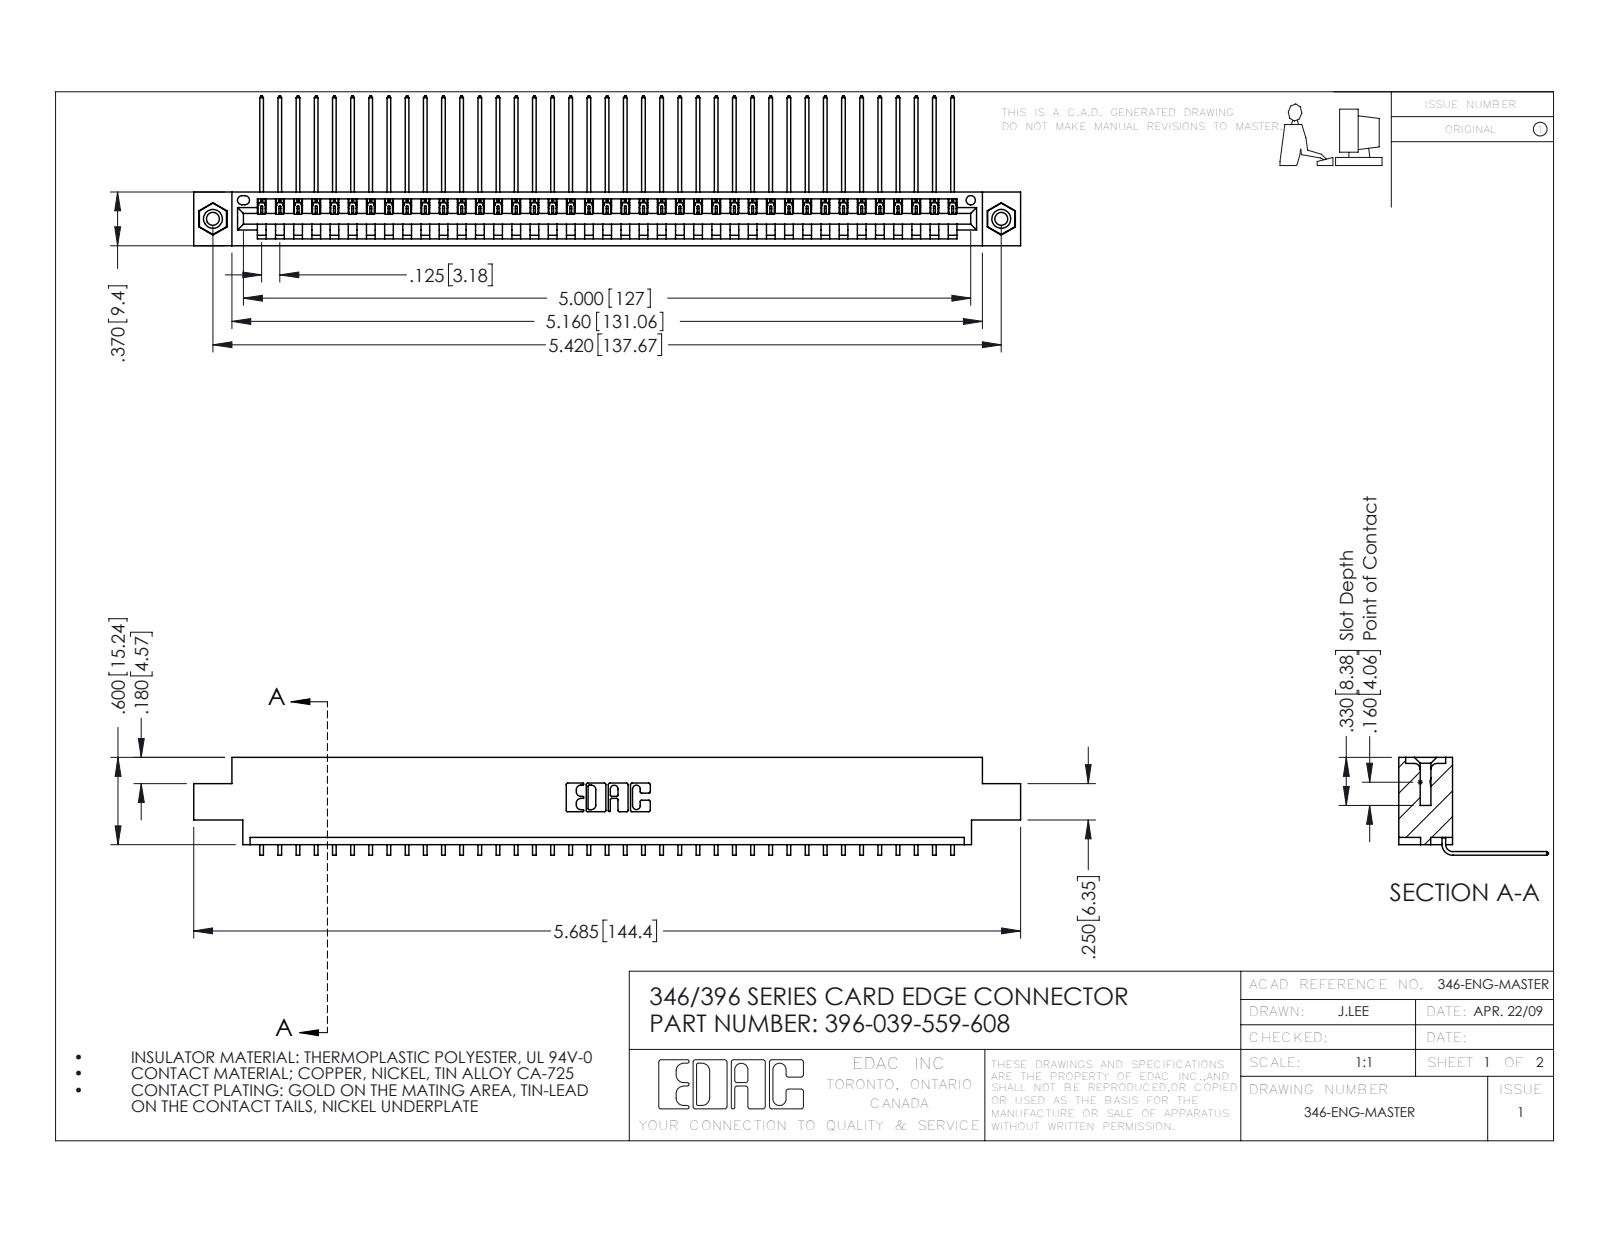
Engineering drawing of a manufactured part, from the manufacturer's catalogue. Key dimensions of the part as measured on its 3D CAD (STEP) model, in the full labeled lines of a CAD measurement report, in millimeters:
Part name (STEP PRODUCT): 346 Part_0.170 Offset - 0.156 Dia-TI; 345-292-001_558 559 Tail - 1; 345-250-001_345-250-003-102; 396-039-559-608
STEP written by: SolidWorks 2016 (CONFIG_CONTROL_DESIGN)
Units: millimetres
Bodies: 42 solids, 2526 faces (1750 planar, 760 cylindrical, 16 other)
Overall size (bounding box): 144.4 × 26.2 × 17.1
Volume: 13 800 mm³ · Surface area: 18 140 mm²
Round holes (diameter × count): ⌀2.3 ×2, ⌀3.2 ×2, ⌀4 ×2, ⌀1.6 ×1
Round bosses / shafts (diameter × count): ⌀3.9 ×2
Partial cylindrical surfaces — rounded edges, fillets, slot ends (radius × count): R0.2 ×78, R0.3 ×22, R0.2 ×6, R0.8 ×6, R0.7 ×3, R0.8 ×2, R1 ×2, R0.4 ×1
Main face-to-face distances: 1.2, 8.2, 9.4, 0.6, 6.4, 1.8, 5.6, 3.8, 7.6, 2.5
Hole centre spacings: 6.2, 132.4, 137.7
